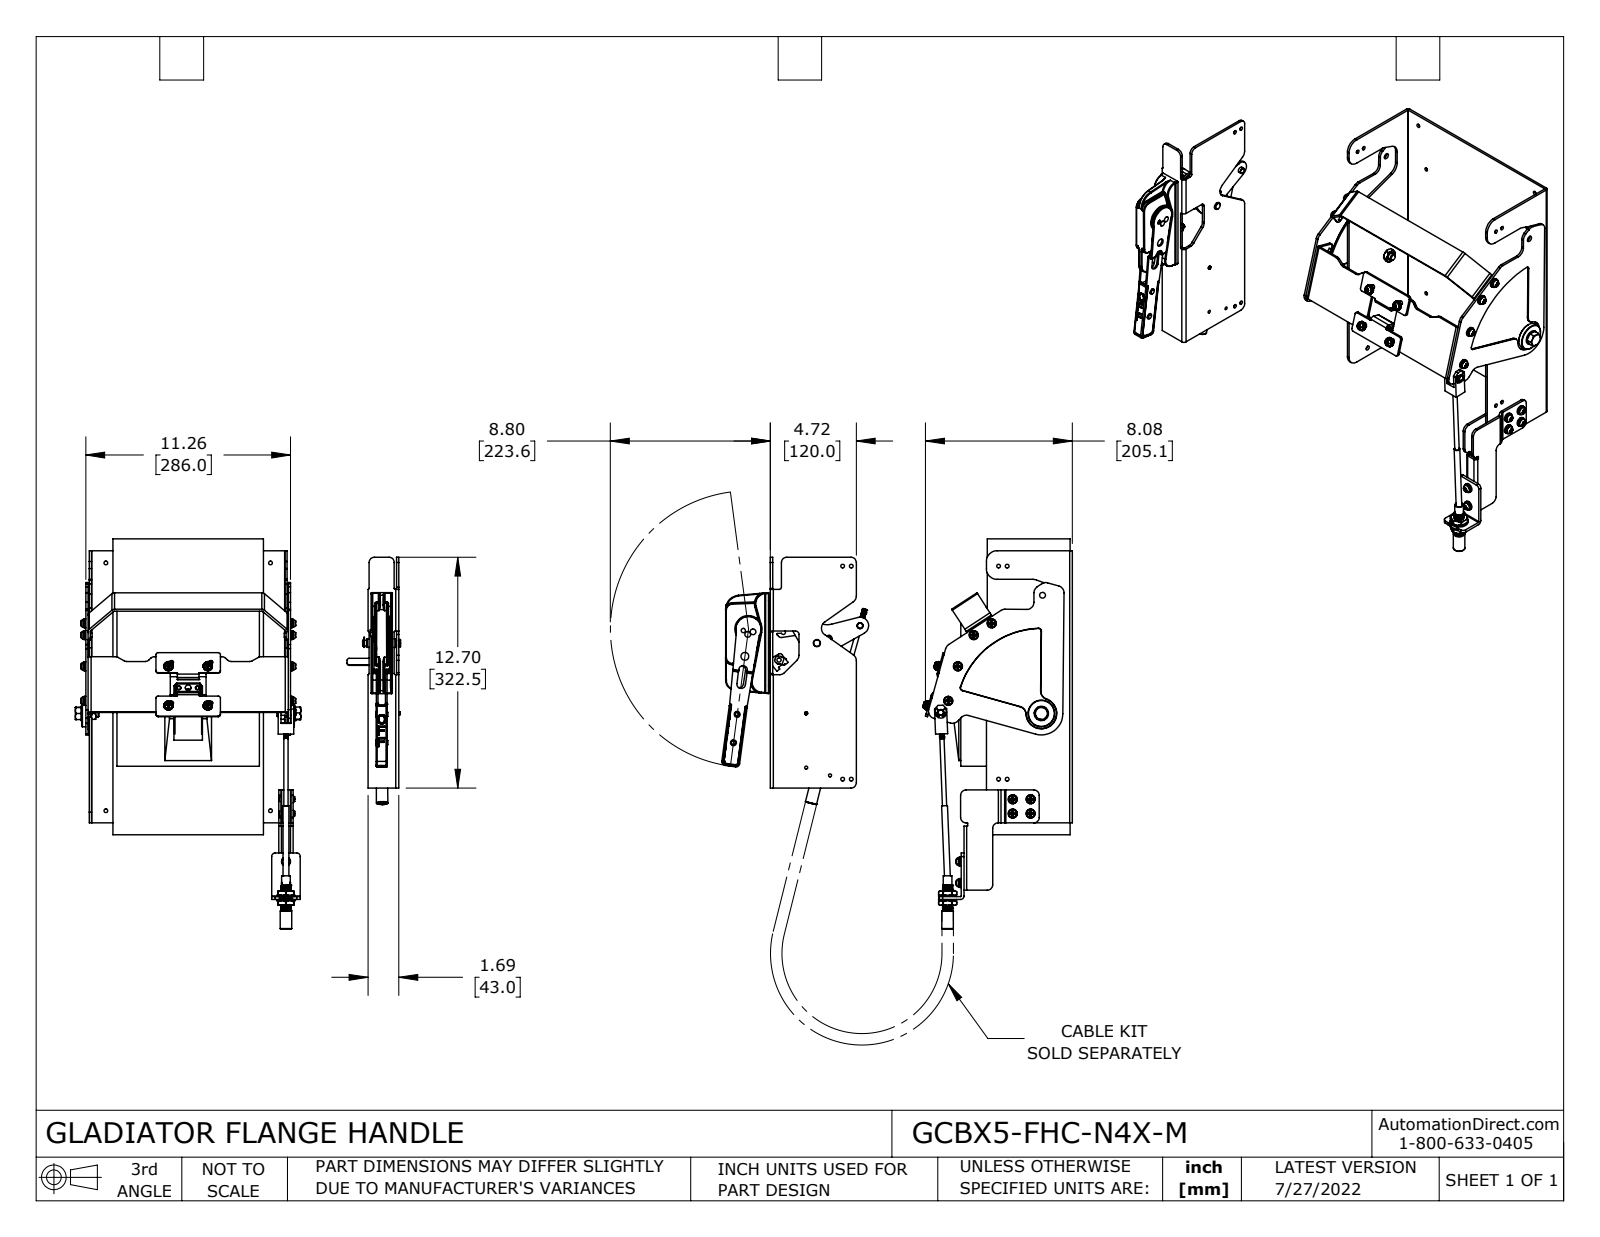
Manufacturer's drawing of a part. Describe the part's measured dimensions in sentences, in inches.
The part is named "GCBX5-FHC-N4X-M; GCBX5-FHC-N4X-M_2; GCBX5-FHC-N4X-M_1; GCBX5-FHC-N4X-M_MCCB". Its 3-D file was written by "SolidWorks 2021 (CONFIG_CONTROL_DESIGN)". It is 98 solids with 4613 faces: 1724 planar, 2103 cylindrical and 786 other. Overall it measures 21.437 by 19.273 by 17.887 inches. Its volume is 801.3 cubic inches and its surface area 2 026 square inches. Round holes: 22 of diameter 0.24, 18 of diameter 0.26, 13 of diameter 0.169, 10 of diameter 0.209, 9 of diameter 0.197, 9 of diameter 0.319, 8 of diameter 0.205, 7 of diameter 0.244, 5 of diameter 0.236, 4 of diameter 0.161, 3 of diameter 0.217, 3 of diameter 0.394. Round bosses or shafts: 25 of diameter 0.236, 18 of diameter 0.492, 18 of diameter 0.48, 18 of diameter 0.413, 10 of diameter 0.315, 3 of diameter 0.984, 3 of diameter 0.472, 3 of diameter 0.394. Partial cylindrical surfaces (rounded edges, fillets, slot ends): 204 of radius 0.02, 170 of radius 0.012, 93 of radius 0.039, 44 of radius 0.118, 34 of radius 0.079, 22 of radius 0.295, 21 of radius 0.394, 20 of radius 0.059. The main face-to-face distances are 0.126, 1.307, 9.575, 10.756, 1.181, 9.449, 0.189, 10.945, 16.902, 6.146. The hole center spacings are 0.512, 2.165, 2.707, 3.119, 8.847, 11.001, 13.856, 0.291.
